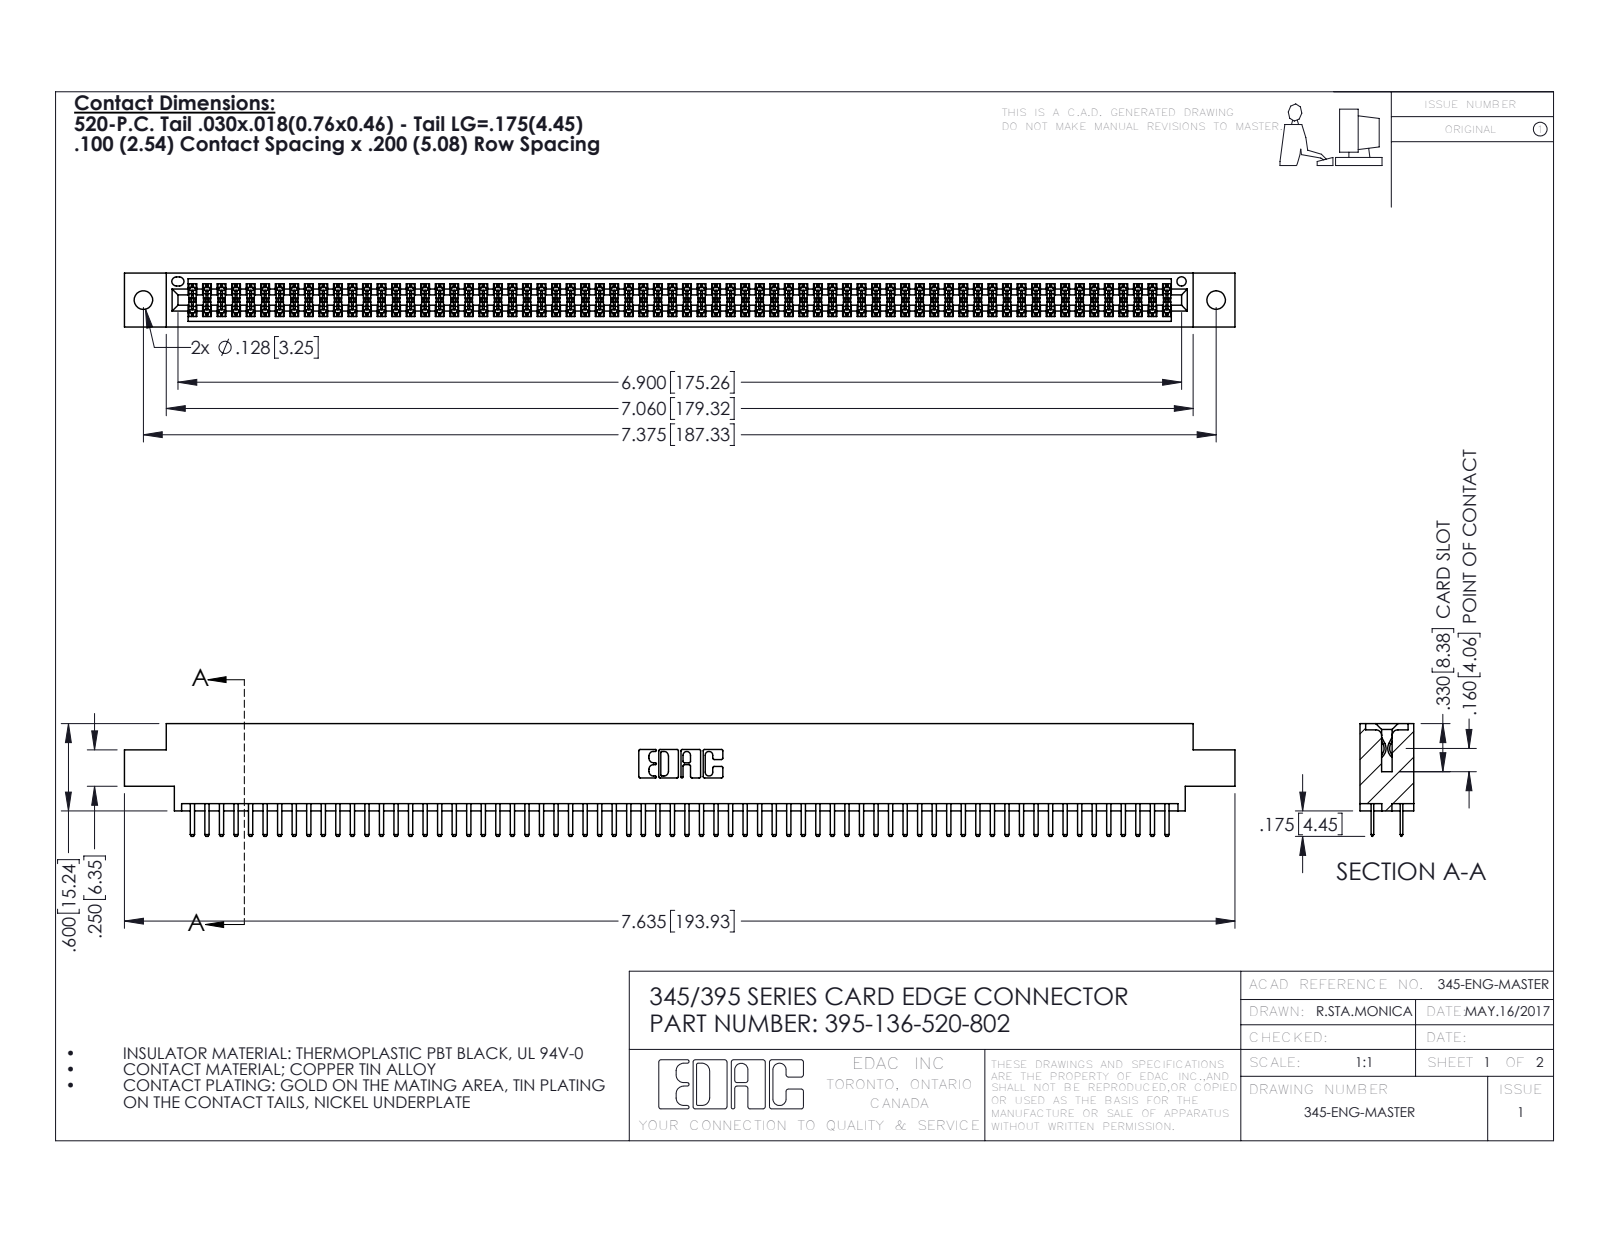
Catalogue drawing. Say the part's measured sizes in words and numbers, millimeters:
The part is named "345-292-001_345-293-120; 395-136-520-802; 345 Part_0.170 Offset - 0.128 Dia". Its 3-D file was written by "SolidWorks 2016 (CONFIG_CONTROL_DESIGN)". It is 137 solids with 7474 faces: 4844 planar, 2630 cylindrical and 0 other. Overall it measures 193.9 by 19.7 by 9.4 millimeters. Its volume is 18 880 cubic millimeters and its surface area 28 140 square millimeters. Round holes: 2 of diameter 3.3, 1 of diameter 1.6. Partial cylindrical surfaces (rounded edges, fillets, slot ends): 204 of radius 0.2, 140 of radius 0.3, 22 of radius 0.3, 6 of radius 0.2, 6 of radius 0.8, 3 of radius 0.7, 2 of radius 0.4, 2 of radius 0.5. The main face-to-face distances are 1.8, 7.6, 5.1, 9.4, 2.5, 6.9, 0.6, 5.7, 0.6, 1.8. The hole center spacings are 6.9, 181.3, 187.3.
